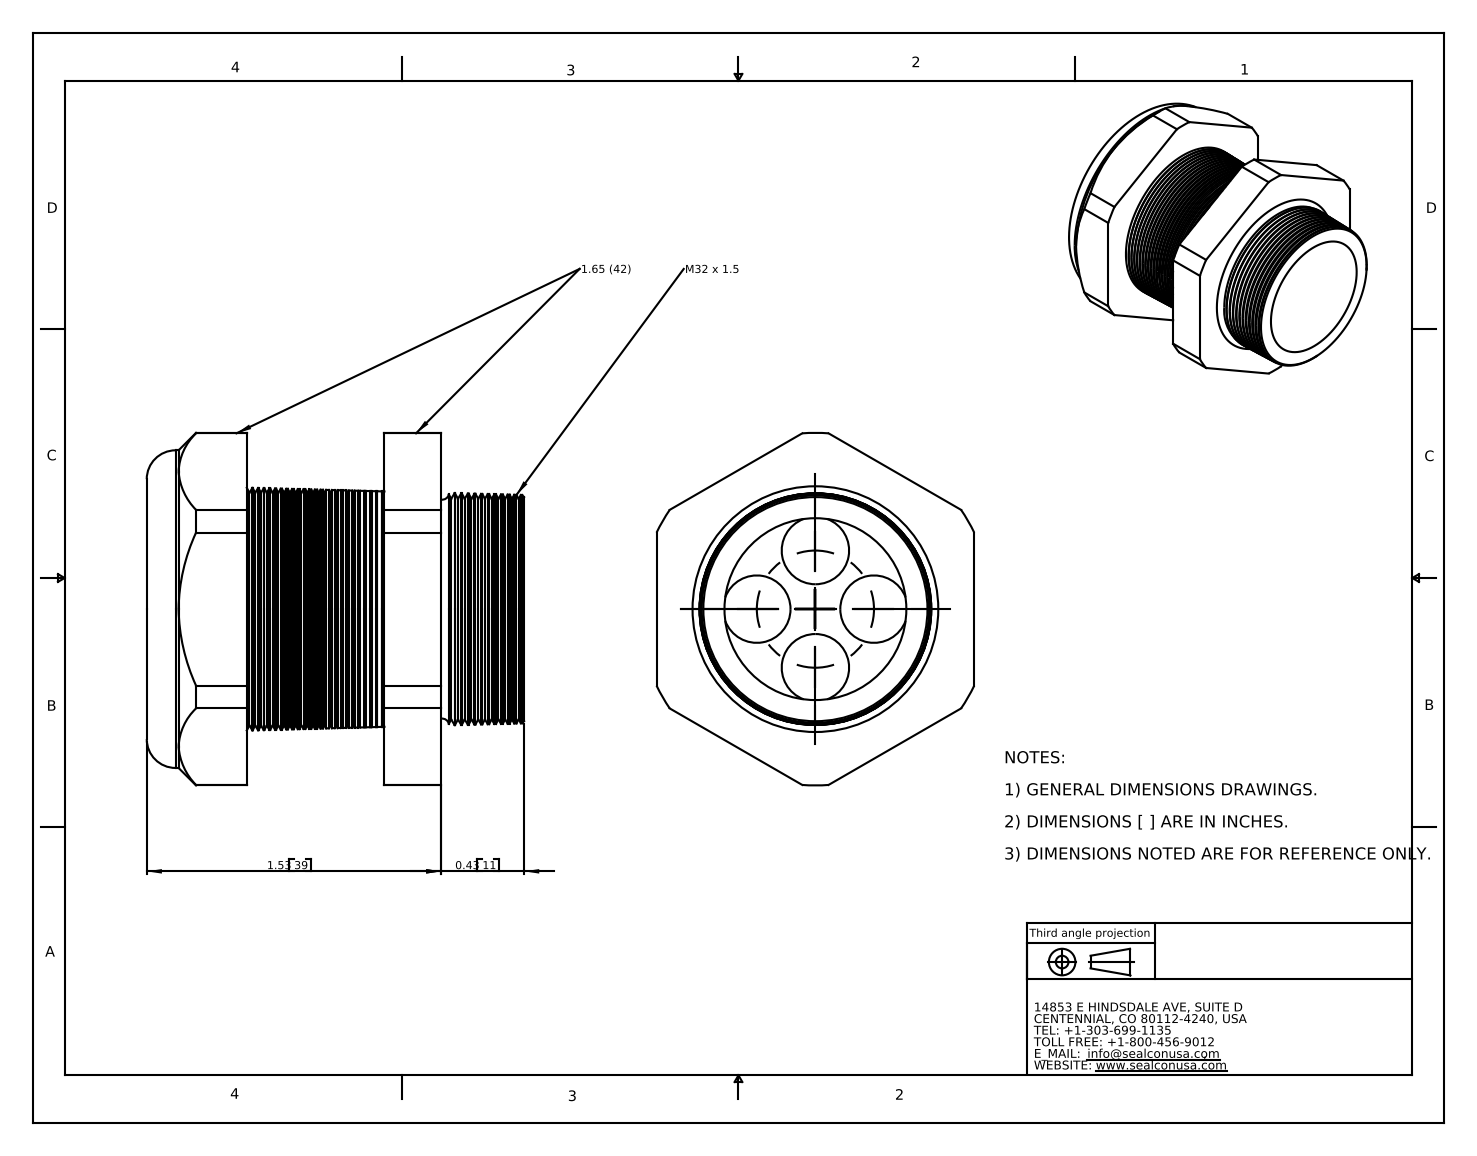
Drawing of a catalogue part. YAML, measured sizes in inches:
part_name: "CD32M2-BK"
step_written_by: "SolidWorks 2007 (CONFIG_CONTROL_DESIGN)"
units: inches
bodies: {solids: 2, faces: 279, planar: 21, cylindrical: 28, other: 230}
overall_size: [1.96, 1.831, 1.65]
volume: 1.891
surface_area: 27.34
round_holes:
  - {diameter: 0.35, count: 4}
  - {diameter: 0.96, count: 1}
  - {diameter: 0.98, count: 1}
round_bosses_or_shafts:
  - {diameter: 1.65, count: 1}
partial_cylinders:
  - {radius: 0.916, count: 1}
face_to_face_distances: [0.715, 1.011, 0.295, 1.65, 0.52, 1.235, 1.53, 1.65, 0.5, 0.02]
hole_center_spacings: [0.304, 0.43, 0.609]
